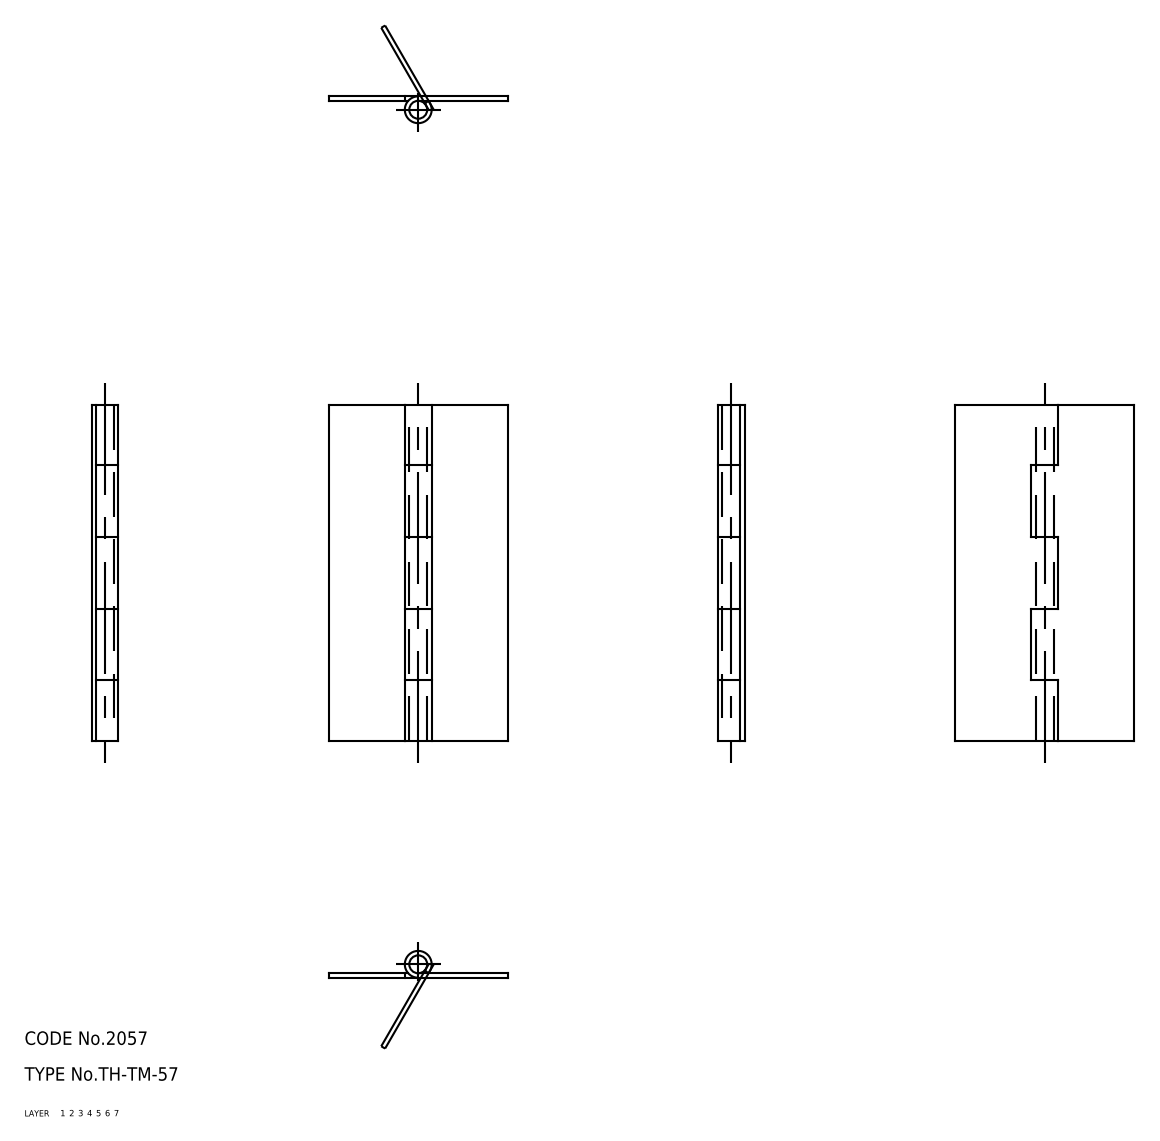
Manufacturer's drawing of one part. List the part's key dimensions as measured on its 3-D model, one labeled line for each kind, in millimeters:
Part name (STEP PRODUCT): hinge piece_B; hinge piece_A; shaft; TH_TM_57_24263_36
STEP written by: CADfix (AUTOMOTIVE_DESIGN)
Units: millimetres
Bodies: 3 solids, 42 faces (0 planar, 0 cylindrical, 42 other)
Overall size (bounding box): 75 × 40 × 6
Volume: 4 736 mm³ · Surface area: 9 085 mm²
